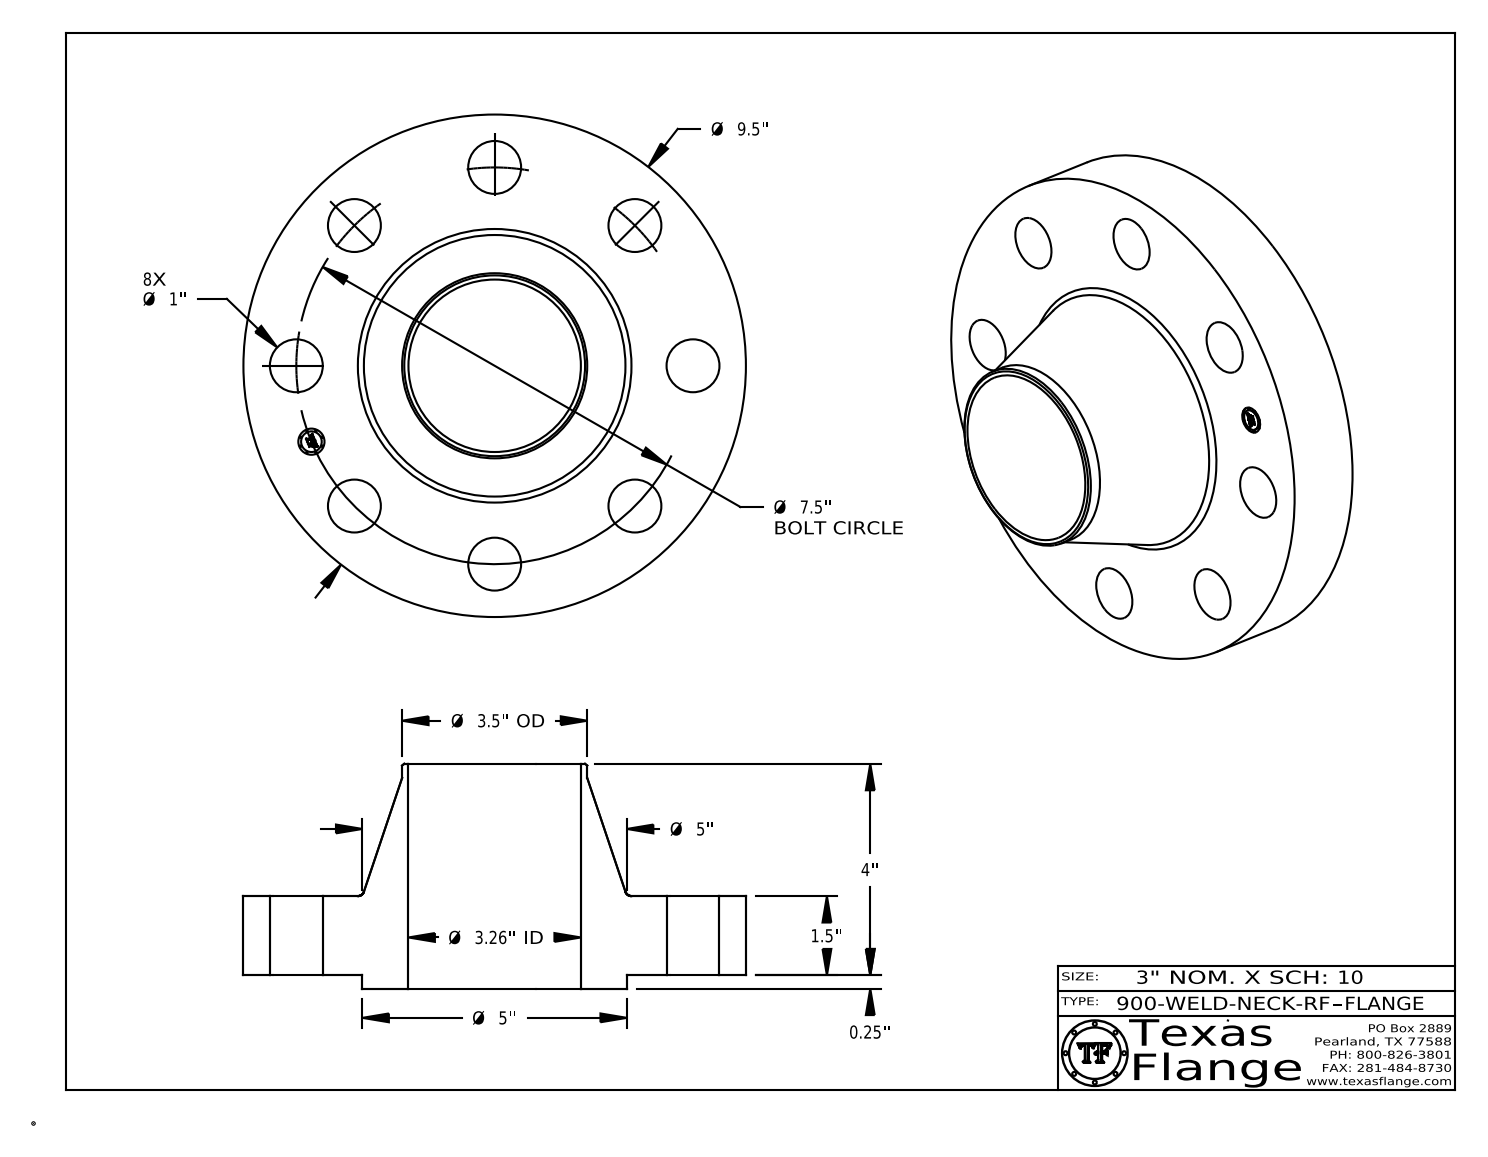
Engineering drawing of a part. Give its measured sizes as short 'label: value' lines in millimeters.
name: 900-WELD-NECK-RF
written by: CATIA V5 STEP AP214 (AUTOMOTIVE_DESIGN)
unit: mm
bodies: 1 solid, 419 faces (369 planar, 44 cylindrical, 6 other)
size: 241.3 × 241.3 × 108
volume: 1 653 000 mm³; area: 171 800 mm²
holes: 8× ⌀25.4, 1× ⌀12.6, 1× ⌀82.8
bosses: 8× ⌀0.8, 1× ⌀241.3, 1× ⌀127, 1× ⌀88.9, 1× ⌀9.9
face distances: 38.1, 6.4, 44.5, 108, 101.6, 63.5, 0.4, 44.1, 37.7, 63.9
hole spacings: 95.3, 72.9, 134.7, 176, 37.2, 158.4, 186.8, 190.5
